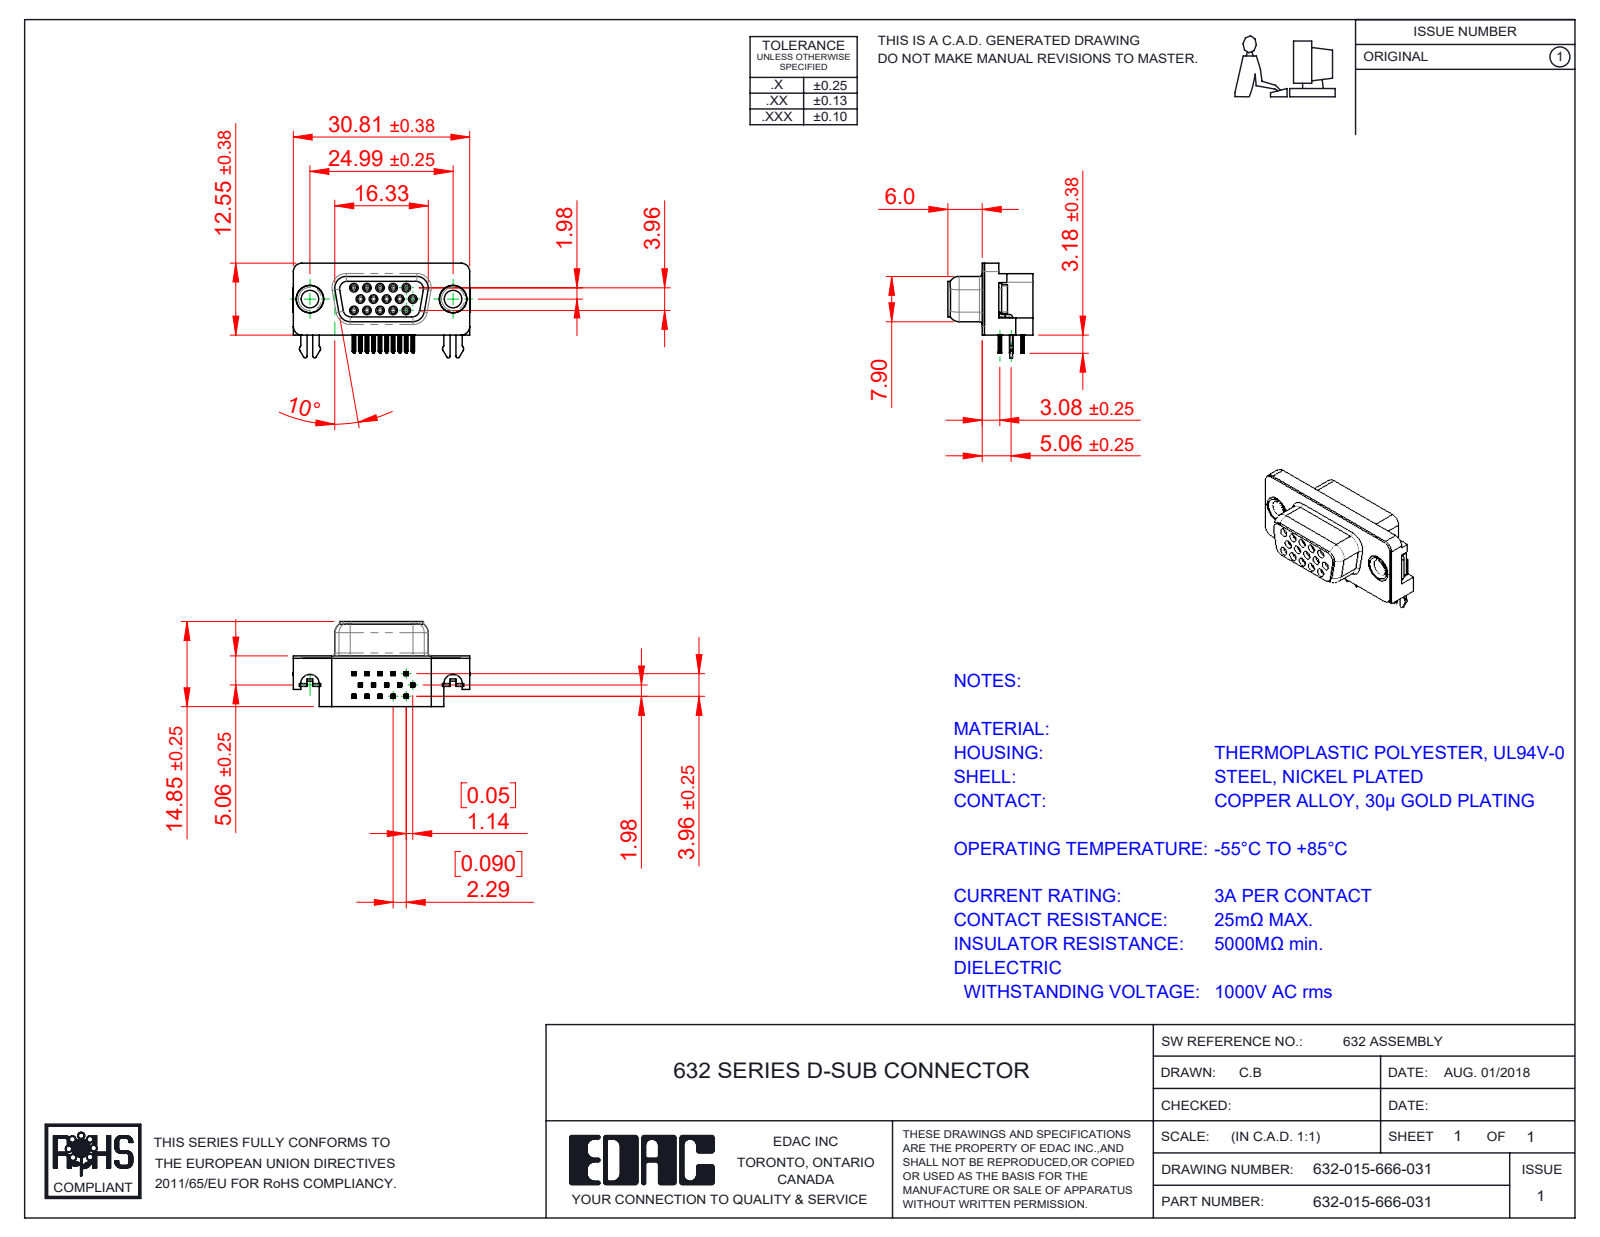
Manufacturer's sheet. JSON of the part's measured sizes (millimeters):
{"part_name": "632-015-666-031; 632 Thru Hole Rivet; 632 2 Prong Board Lock; 632 Contact Top (+4 more)", "step_written_by": "SolidWorks 2016 (CONFIG_CONTROL_DESIGN)", "units": "millimeters", "bodies": {"solids": 21, "faces": 2298, "planar": 990, "cylindrical": 594, "other": 714}, "overall_size": [30.89, 16.55, 14.85], "volume_mm3": 2908, "surface_area_mm2": 4994, "round_holes": [[0.8, 15], [0.9, 15], [3.05, 2], [4, 2], [4.8, 2], [5, 2]], "round_bosses_or_shafts": [[1.2, 15], [4.9, 2], [4.75, 2], [3.85, 2]], "partial_cylinders_radius": [[0.1, 120], [0.15, 60], [0.35, 30], [0.34, 15], [1, 11], [0.28, 10], [0.5, 10], [0.25, 8]], "face_to_face_distances": [0.4, 1.98, 8.45, 8.85, 2.9, 2.5, 5.95, 6.4, 6.7, 7.05], "hole_center_spacings": [2.28, 2.29, 3.96, 4.57, 6.05, 3.97, 4.58, 6.86]}
